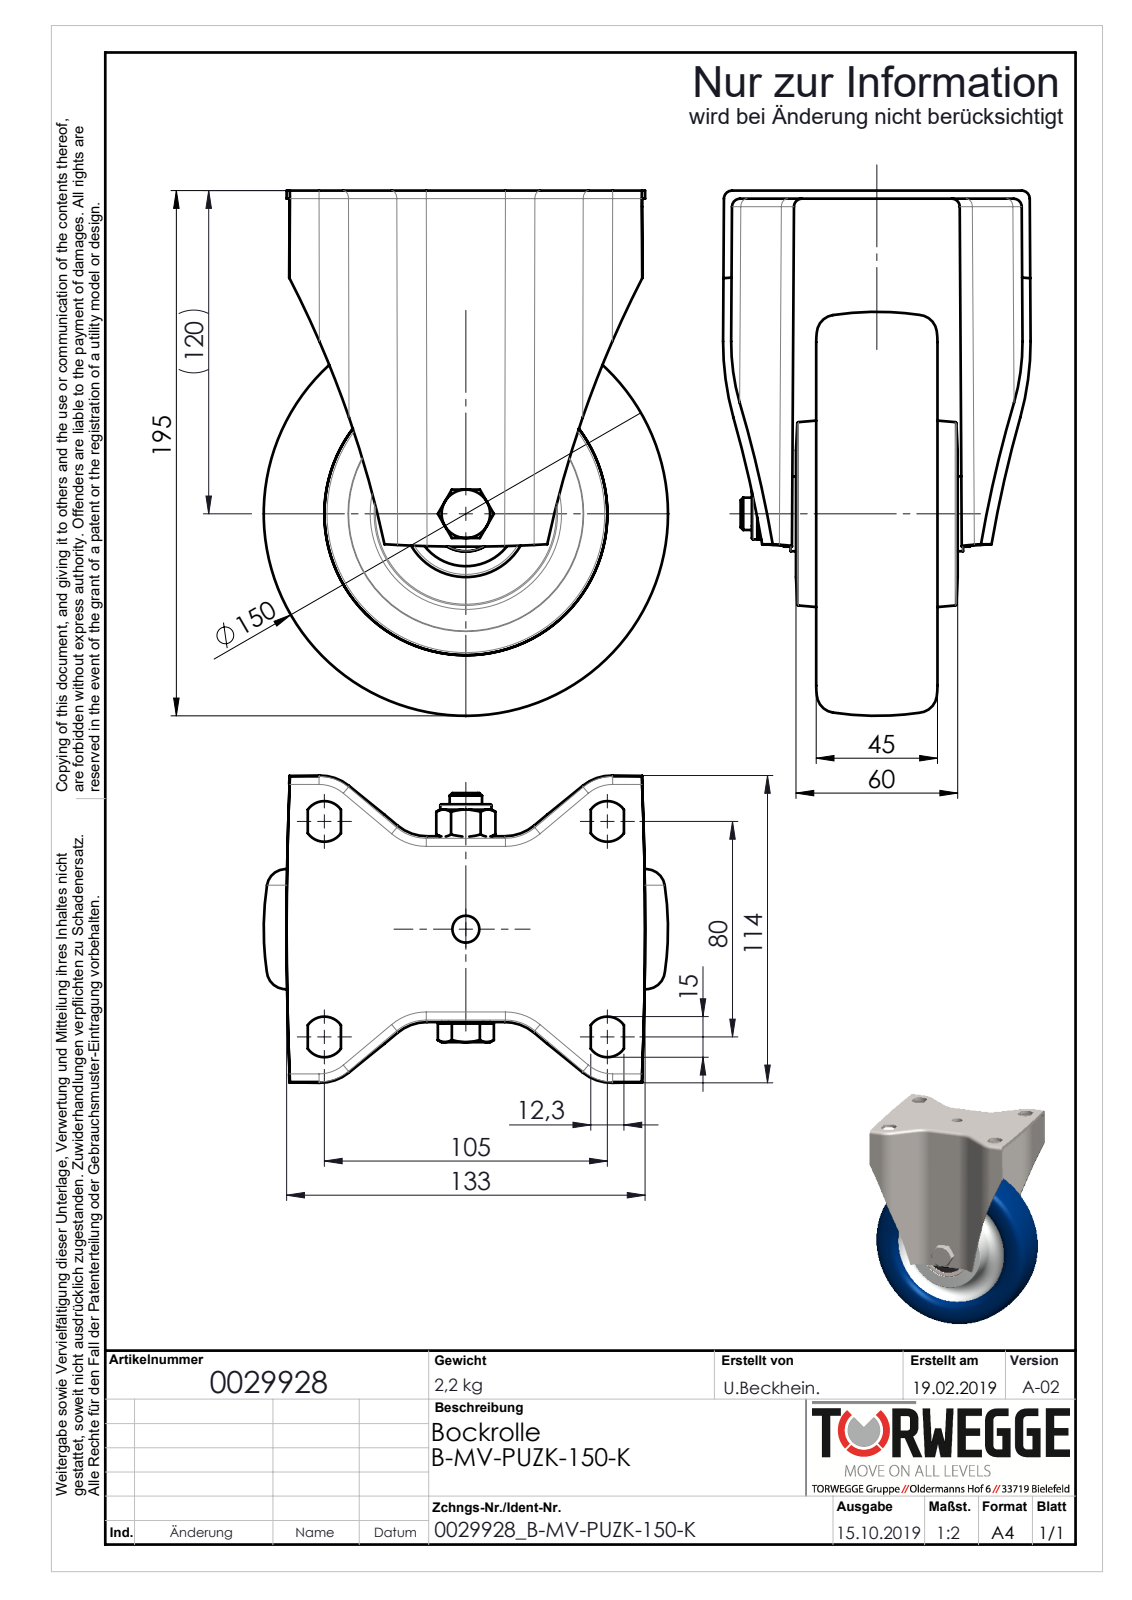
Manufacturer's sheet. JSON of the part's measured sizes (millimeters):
{"part_name": "0029928_B-MV-PUZK-150-K_(A-02)", "step_written_by": "SolidWorks 2018 (AUTOMOTIVE_DESIGN)", "units": "millimeters", "bodies": {"solids": 14, "faces": 489, "planar": 163, "cylindrical": 136, "other": 190}, "overall_size": [195, 150, 114.1], "volume_mm3": 759797, "surface_area_mm2": 248698, "round_holes": [[10, 1], [10.2, 1], [12.3, 1], [12.4, 1], [20, 1], [28.1, 1], [35, 1], [38.9, 1], [131, 1]], "round_bosses_or_shafts": [[47, 1], [27.8, 1], [19.6, 1], [19, 1], [18, 1], [12, 1]], "partial_cylinders_radius": [[3, 16], [17, 8], [7.55, 4], [14, 4], [20, 4], [400, 2], [64.5, 1], [501.25, 1]], "face_to_face_distances": [3, 46, 23, 1, 0.5, 31, 0.8, 13.2, 13.5, 12.7]}
